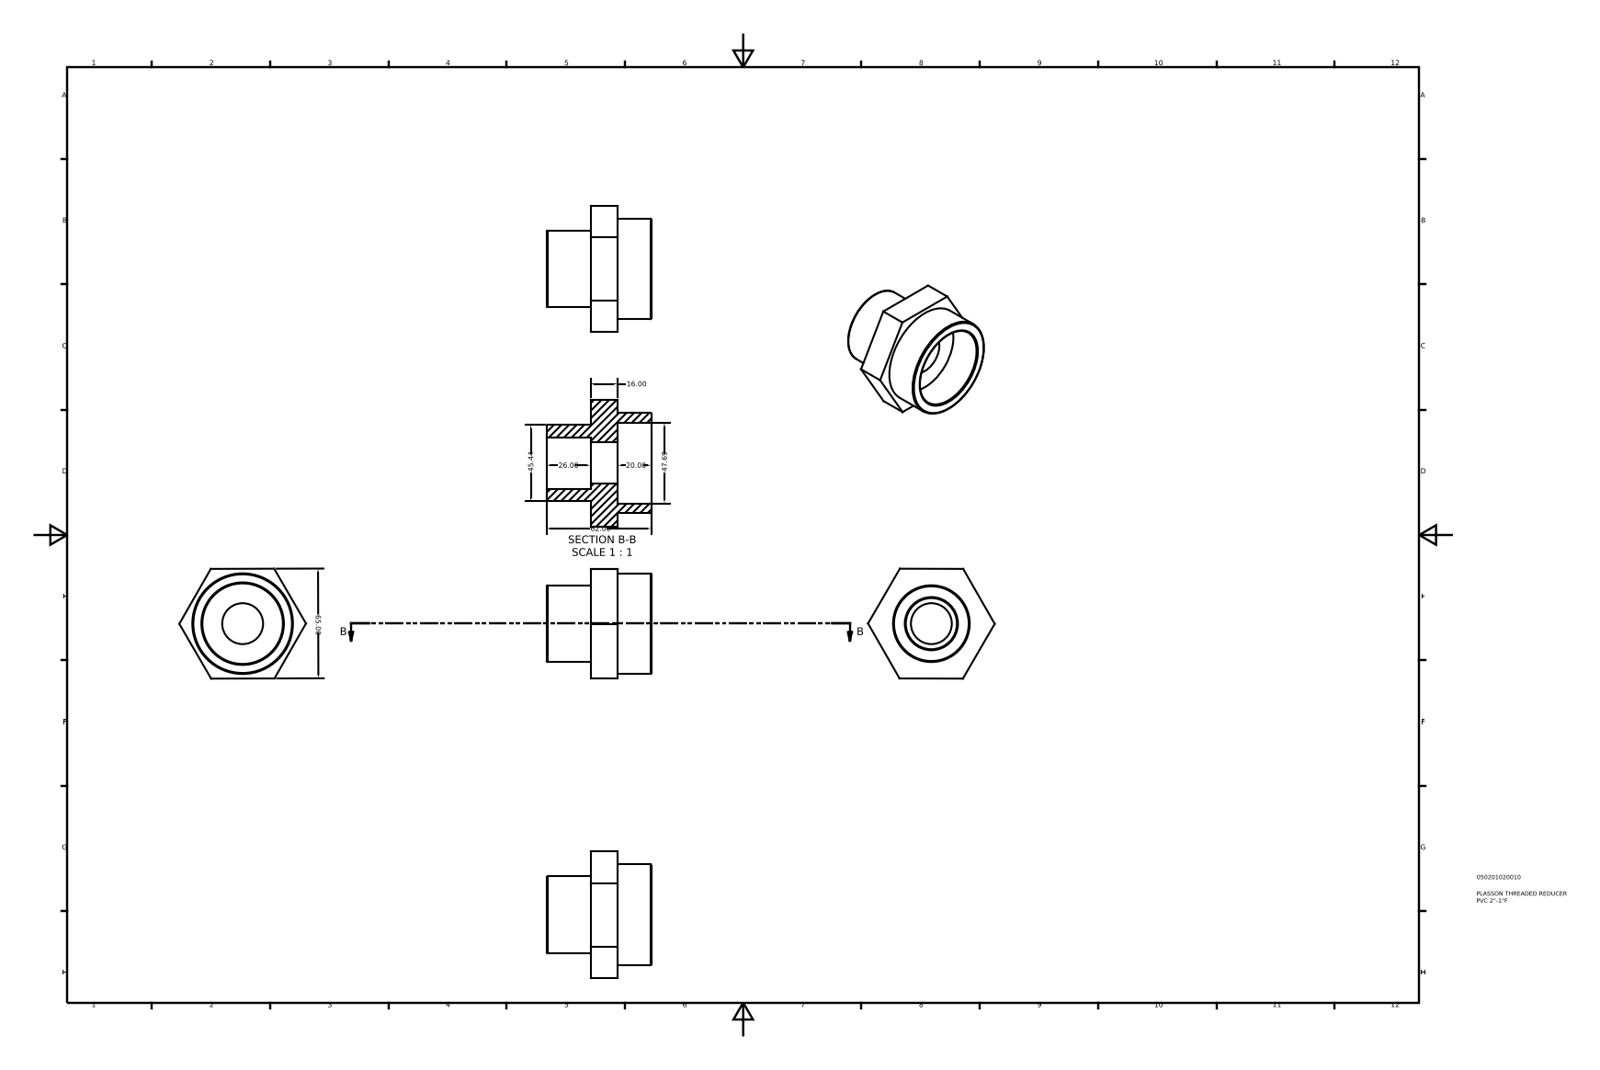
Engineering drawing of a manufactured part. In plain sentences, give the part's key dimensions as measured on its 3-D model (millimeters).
The part is named "050201020010". Its 3-D file was written by "Autodesk Inventor 2015 (AUTOMOTIVE_DESIGN)". It is 1 solid with 21 faces: 12 planar, 5 cylindrical and 4 other. Overall it measures 75.06 by 65.11 by 62 millimeters. Its volume is 94 637 cubic millimeters and its surface area 23 997 square millimeters. Round holes: 1 of diameter 24.23, 1 of diameter 30.29, 1 of diameter 47.69. Round bosses or shafts: 1 of diameter 59.61, 1 of diameter 45.44. The main face-to-face distances are 16, 65.04, 36, 20, 26, 42, 62, 65.
